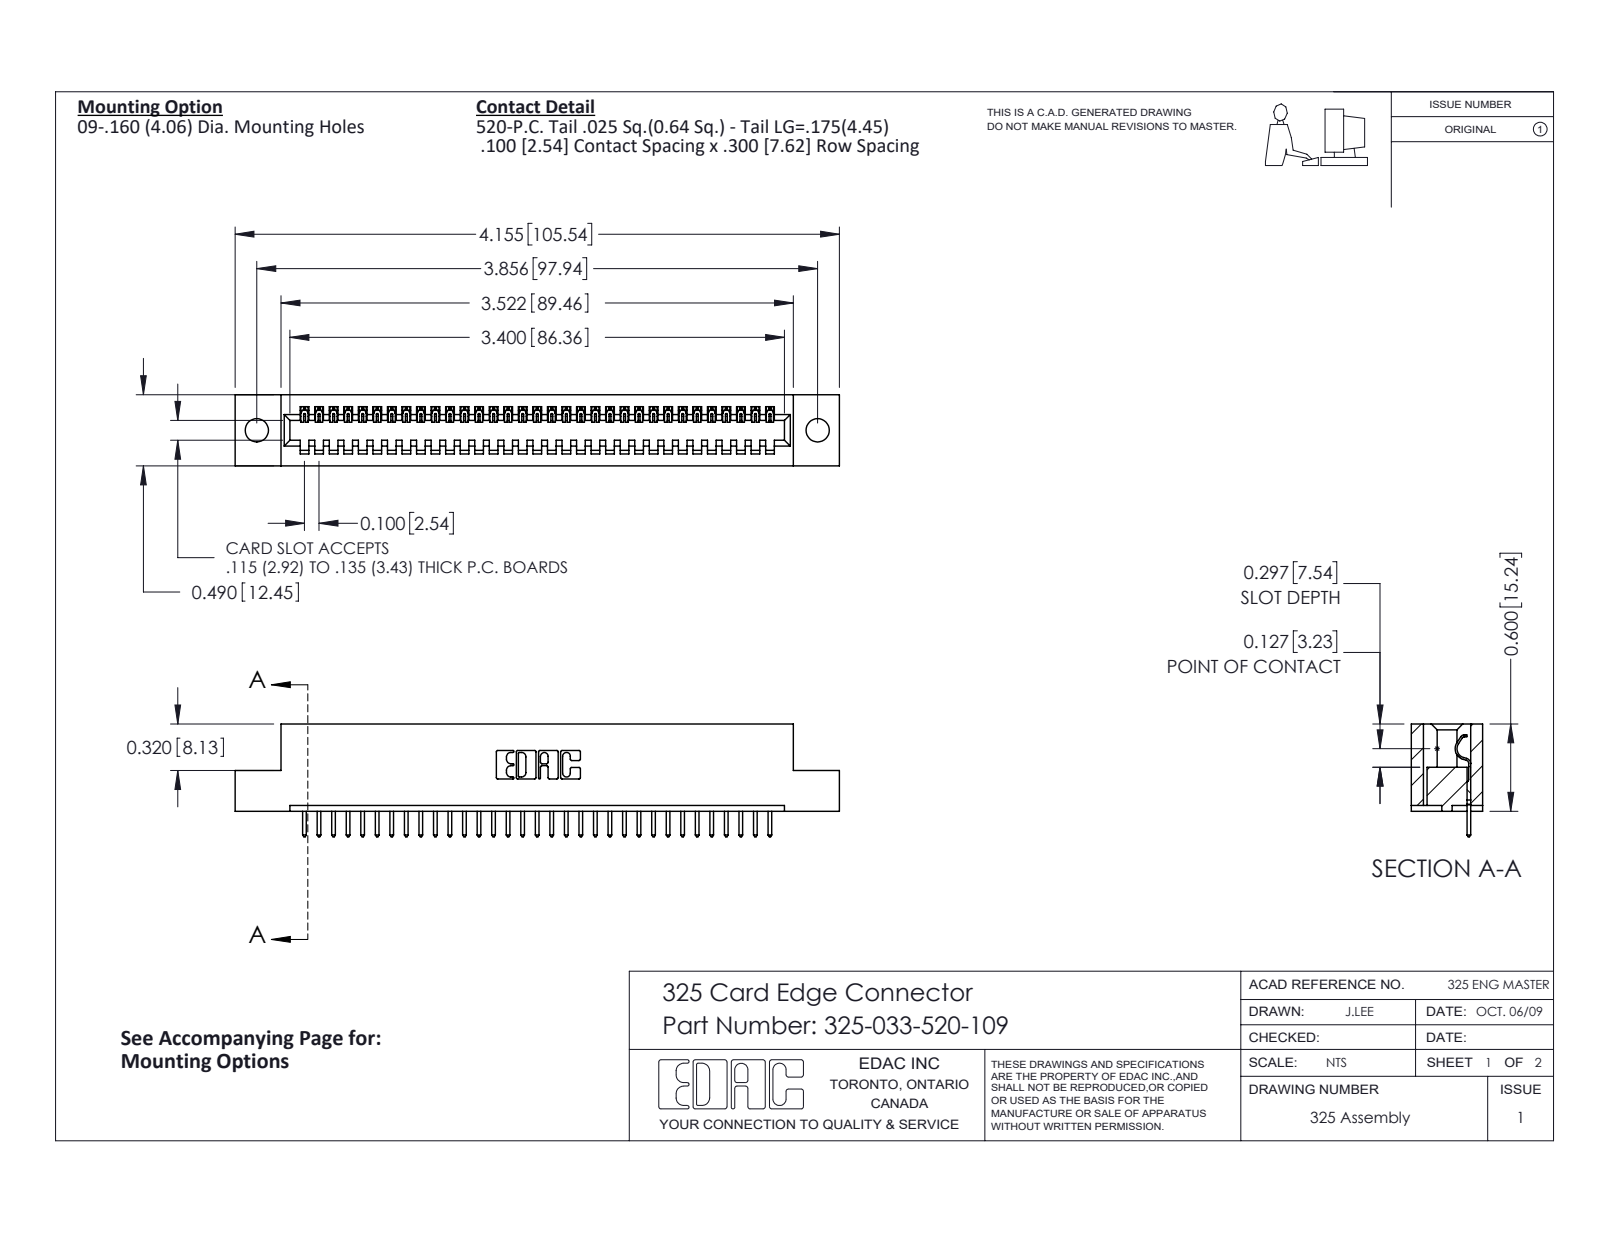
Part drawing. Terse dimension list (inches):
name: 325-033-520-109; 325 Part_.160 TH; 325-292-001_325-293-120
written by: SolidWorks 2016 (CONFIG_CONTROL_DESIGN)
unit: in
bodies: 34 solids, 2028 faces (1456 planar, 572 cylindrical, 0 other)
size: 4.155 × 0.775 × 0.49
volume: 0.794 in³; area: 21.1 in²
holes: 2× ⌀0.16
rounds: 66× R0.006, 66× R0.01, 22× R0.01, 6× R0.007, 6× R0.031, 3× R0.026, 1× R0.014, 1× R0.022
face distances: 0.083, 0.407, 0.49, 0.3, 0.107, 0.383, 0.025, 0.325, 0.56, 0.04
hole spacings: 3.856
